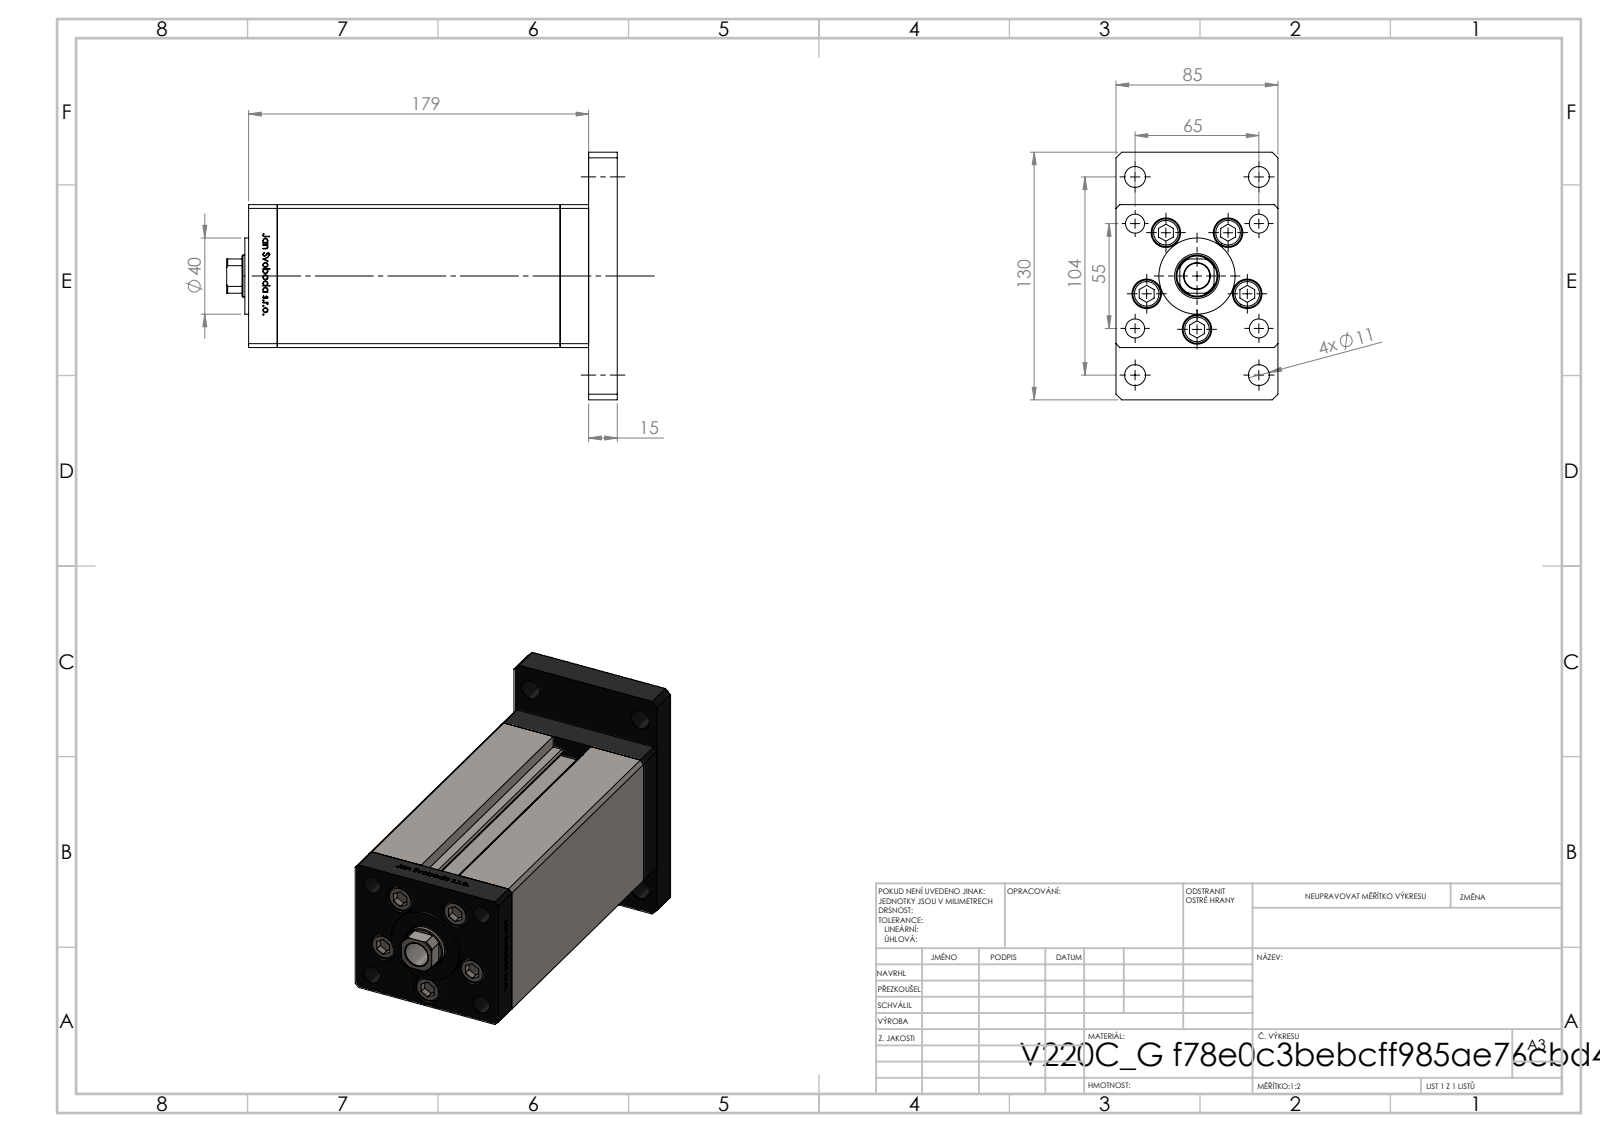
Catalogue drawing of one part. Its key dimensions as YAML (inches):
part_name: "V220C BACK_G; V220C_F; V220C_G_MIDDLE; V220C_VC_G (+2 more)"
step_written_by: "SolidWorks 2019 (CONFIG_CONTROL_DESIGN)"
units: inches
bodies: {solids: 19, faces: 1313, planar: 518, cylindrical: 189, other: 606}
overall_size: [8.071, 5.118, 3.346]
volume: 70.67
surface_area: 306.2
round_holes:
  - {diameter: 0.394, count: 9}
  - {diameter: 0.433, count: 9}
  - {diameter: 0.61, count: 5}
  - {diameter: 0.571, count: 4}
  - {diameter: 0.079, count: 2}
  - {diameter: 0.518, count: 2}
  - {diameter: 0.531, count: 1}
  - {diameter: 0.866, count: 1}
  - {diameter: 0.925, count: 1}
  - {diameter: 2.205, count: 1}
round_bosses_or_shafts:
  - {diameter: 0.315, count: 9}
  - {diameter: 0.571, count: 5}
  - {diameter: 1.575, count: 1}
partial_cylinders:
  - {radius: 0.037, count: 2}
  - {radius: 0.413, count: 1}
face_to_face_distances: [0.591, 3.346, 6.437, 7.028, 2.953, 5.846, 1.181, 0.079, 6.949, 7.618]
hole_center_spacings: [1.102, 0.965, 1.676, 2.414, 2.559, 2.735, 3.13, 4.043]
